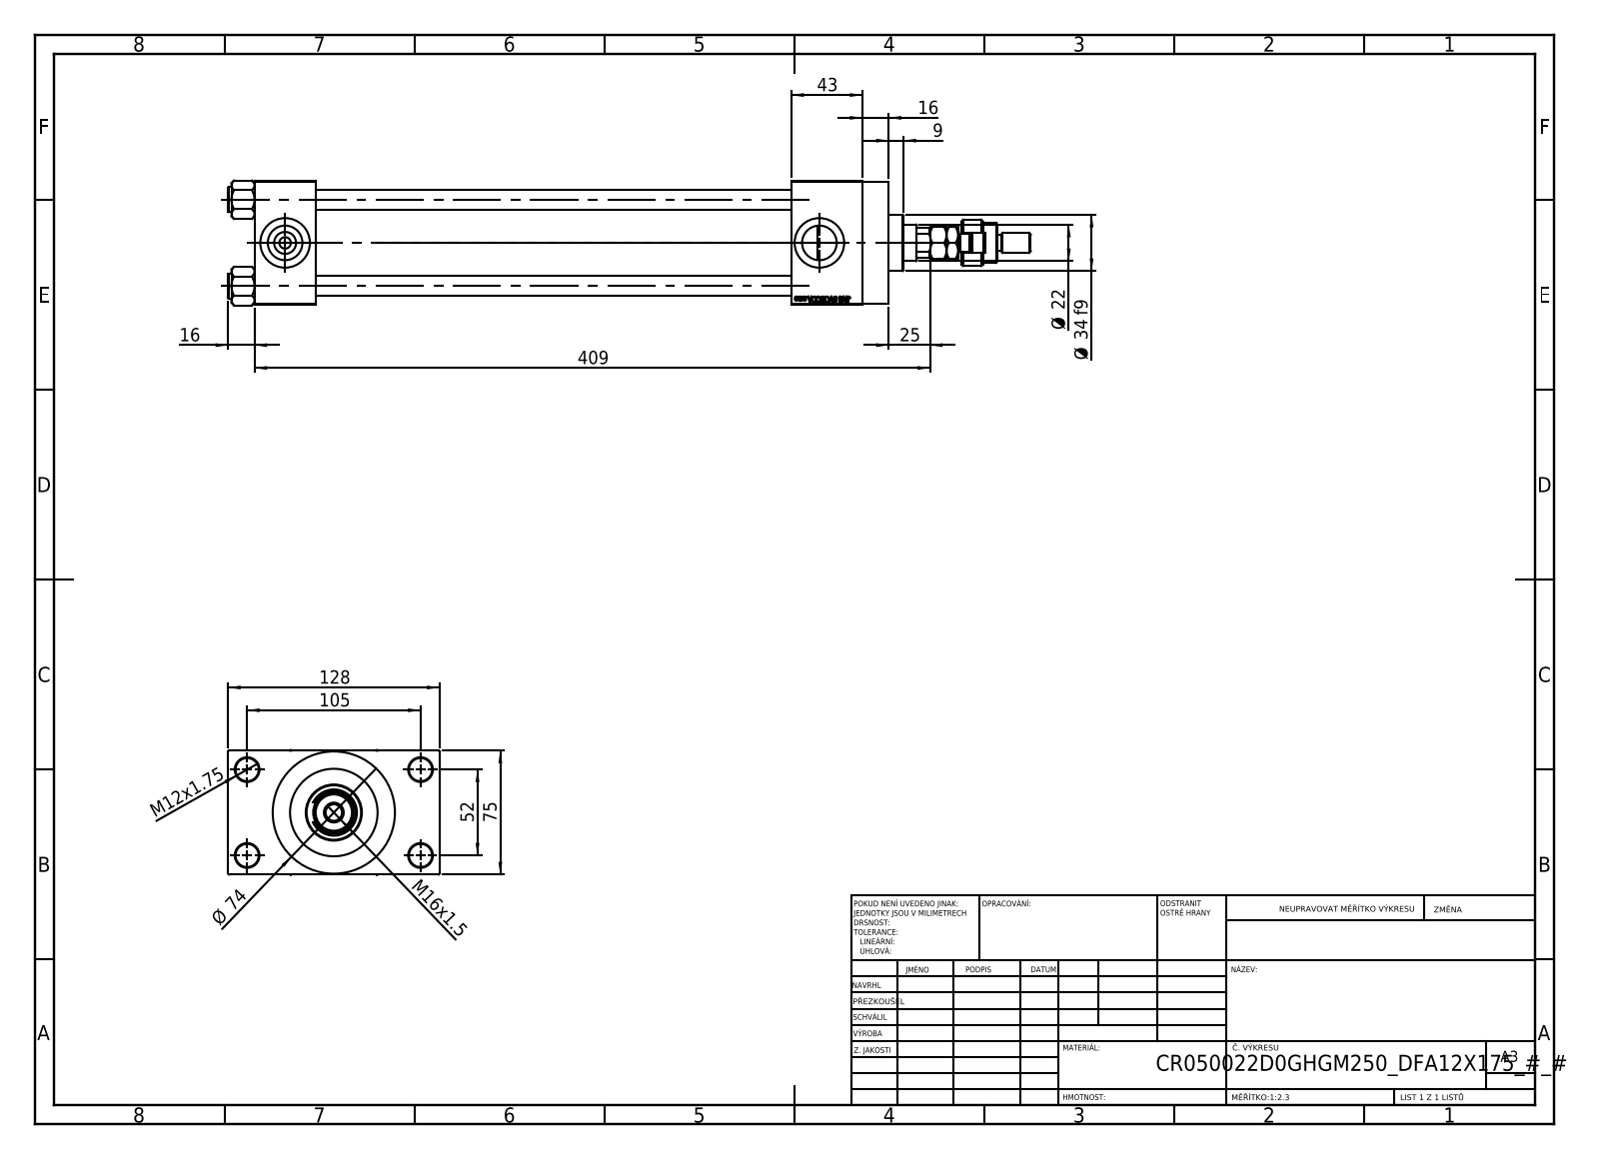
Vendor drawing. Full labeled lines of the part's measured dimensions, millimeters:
Part name (STEP PRODUCT): MFA; V215CR_VCP_D; V215_VC_A; FEMALE_PART_FOR_DFA (+3 more)
STEP written by: SolidWorks 2019 (CONFIG_CONTROL_DESIGN)
Units: millimetres
Bodies: 13 solids, 1188 faces (525 planar, 101 cylindrical, 562 other)
Overall size (bounding box): 486 × 128 × 75.54
Volume: 1 122 000 mm³ · Surface area: 300 980 mm²
Round holes (diameter × count): ⌀12 ×4, ⌀14 ×4, ⌀7 ×2, ⌀20.96 ×2, ⌀30 ×2, ⌀10.5 ×1, ⌀22 ×1, ⌀25 ×1, ⌀41 ×1, ⌀50 ×1, ⌀53 ×1
Round bosses / shafts (diameter × count): ⌀15 ×4, ⌀74 ×1, ⌀56 ×1, ⌀34 ×1, ⌀28 ×1, ⌀24 ×1, ⌀18 ×1, ⌀12 ×1
Partial cylindrical surfaces — rounded edges, fillets, slot ends (radius × count): R9.75 ×1, R10.5 ×1
Main face-to-face distances: 75, 288, 37, 325, 26.5, 368, 331, 43, 16, 101.5
Hole centre spacings: 26.35, 36.98, 52.3, 58.43, 58.59, 78.65, 94.37, 52
